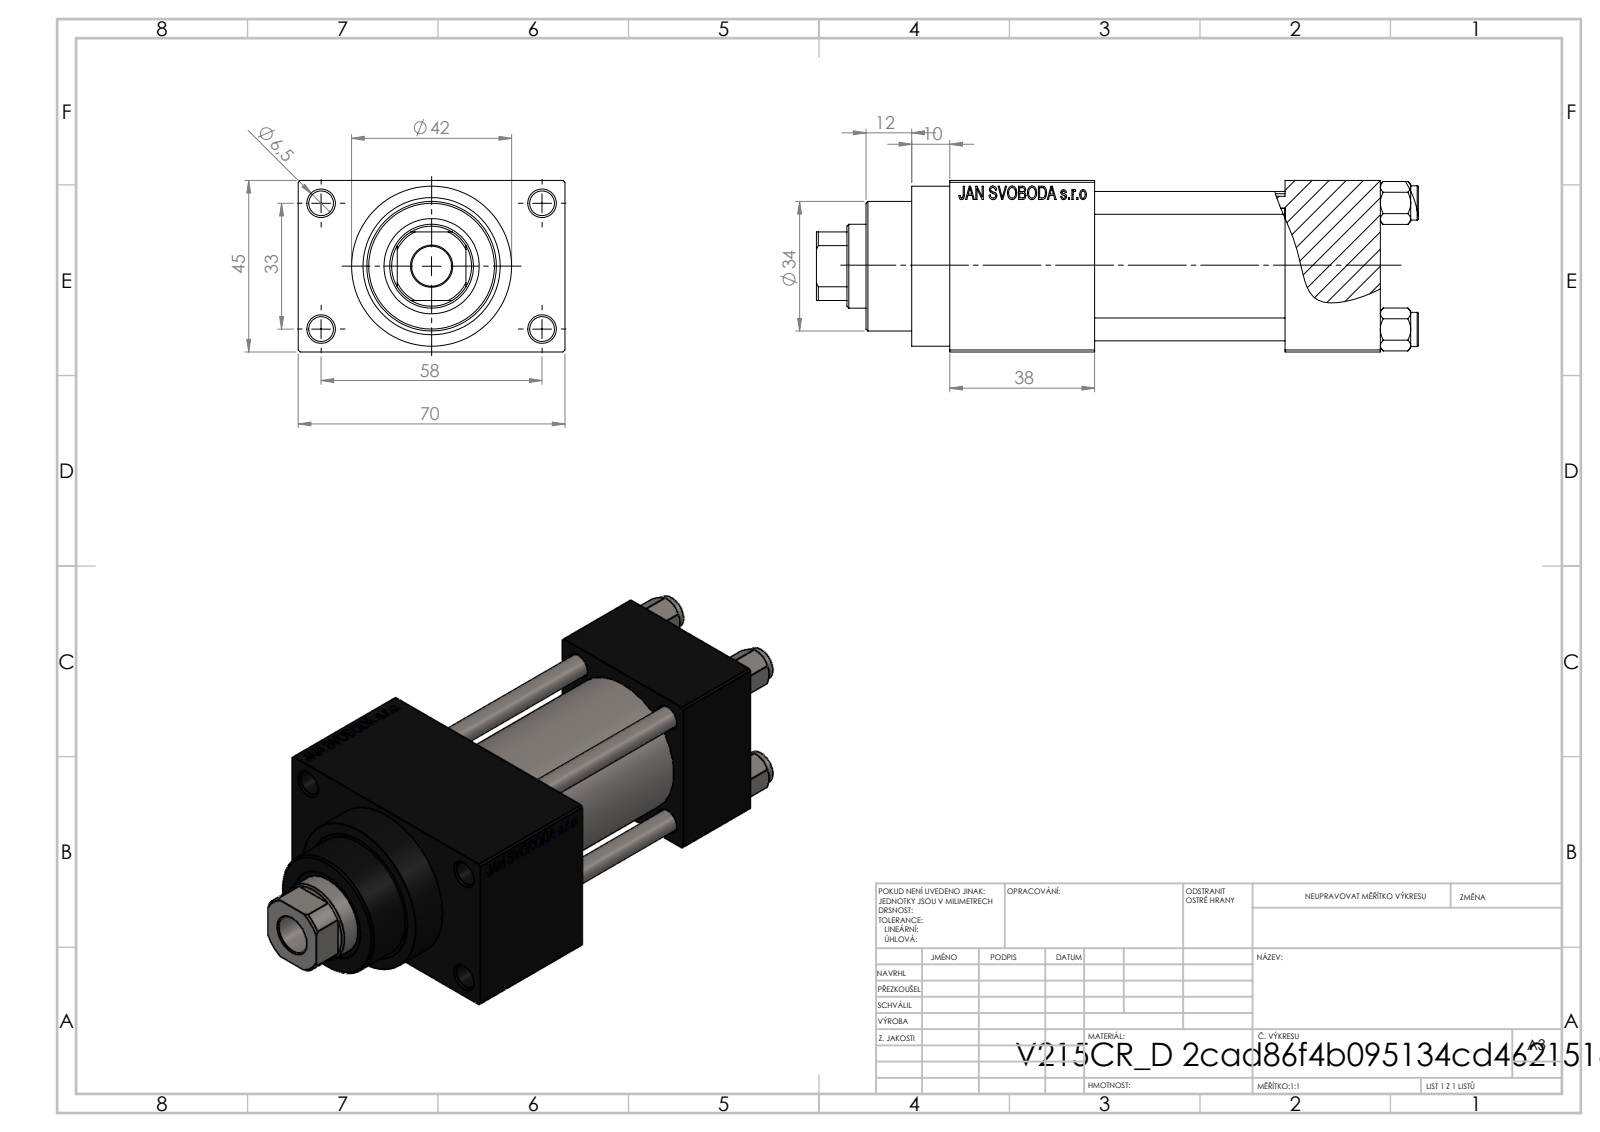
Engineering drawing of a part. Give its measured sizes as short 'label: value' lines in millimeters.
name: V215_VC_A; V215CR_D_Body; NUT_M5_D; V215CR_D_TYCINKA (+1 more)
written by: SolidWorks 2019 (CONFIG_CONTROL_DESIGN)
unit: mm
bodies: 11 solids, 1104 faces (496 planar, 88 cylindrical, 520 other)
size: 158 × 70 × 45
volume: 242 876 mm³; area: 79 884 mm²
holes: 4× ⌀6, 4× ⌀6.5, 2× ⌀7, 2× ⌀13.16, 2× ⌀20, 1× ⌀10.5, 1× ⌀22, 1× ⌀24, 1× ⌀25, 1× ⌀32, 1× ⌀33
bosses: 4× ⌀9, 1× ⌀42, 1× ⌀38, 1× ⌀34
rounds: 1× R10.5
face distances: 45, 25, 50, 12.5, 75, 57.5, 88, 38, 113, 70
hole spacings: 12.4, 23.48, 33.2, 33.37, 35.35, 45.6, 56.35, 33
